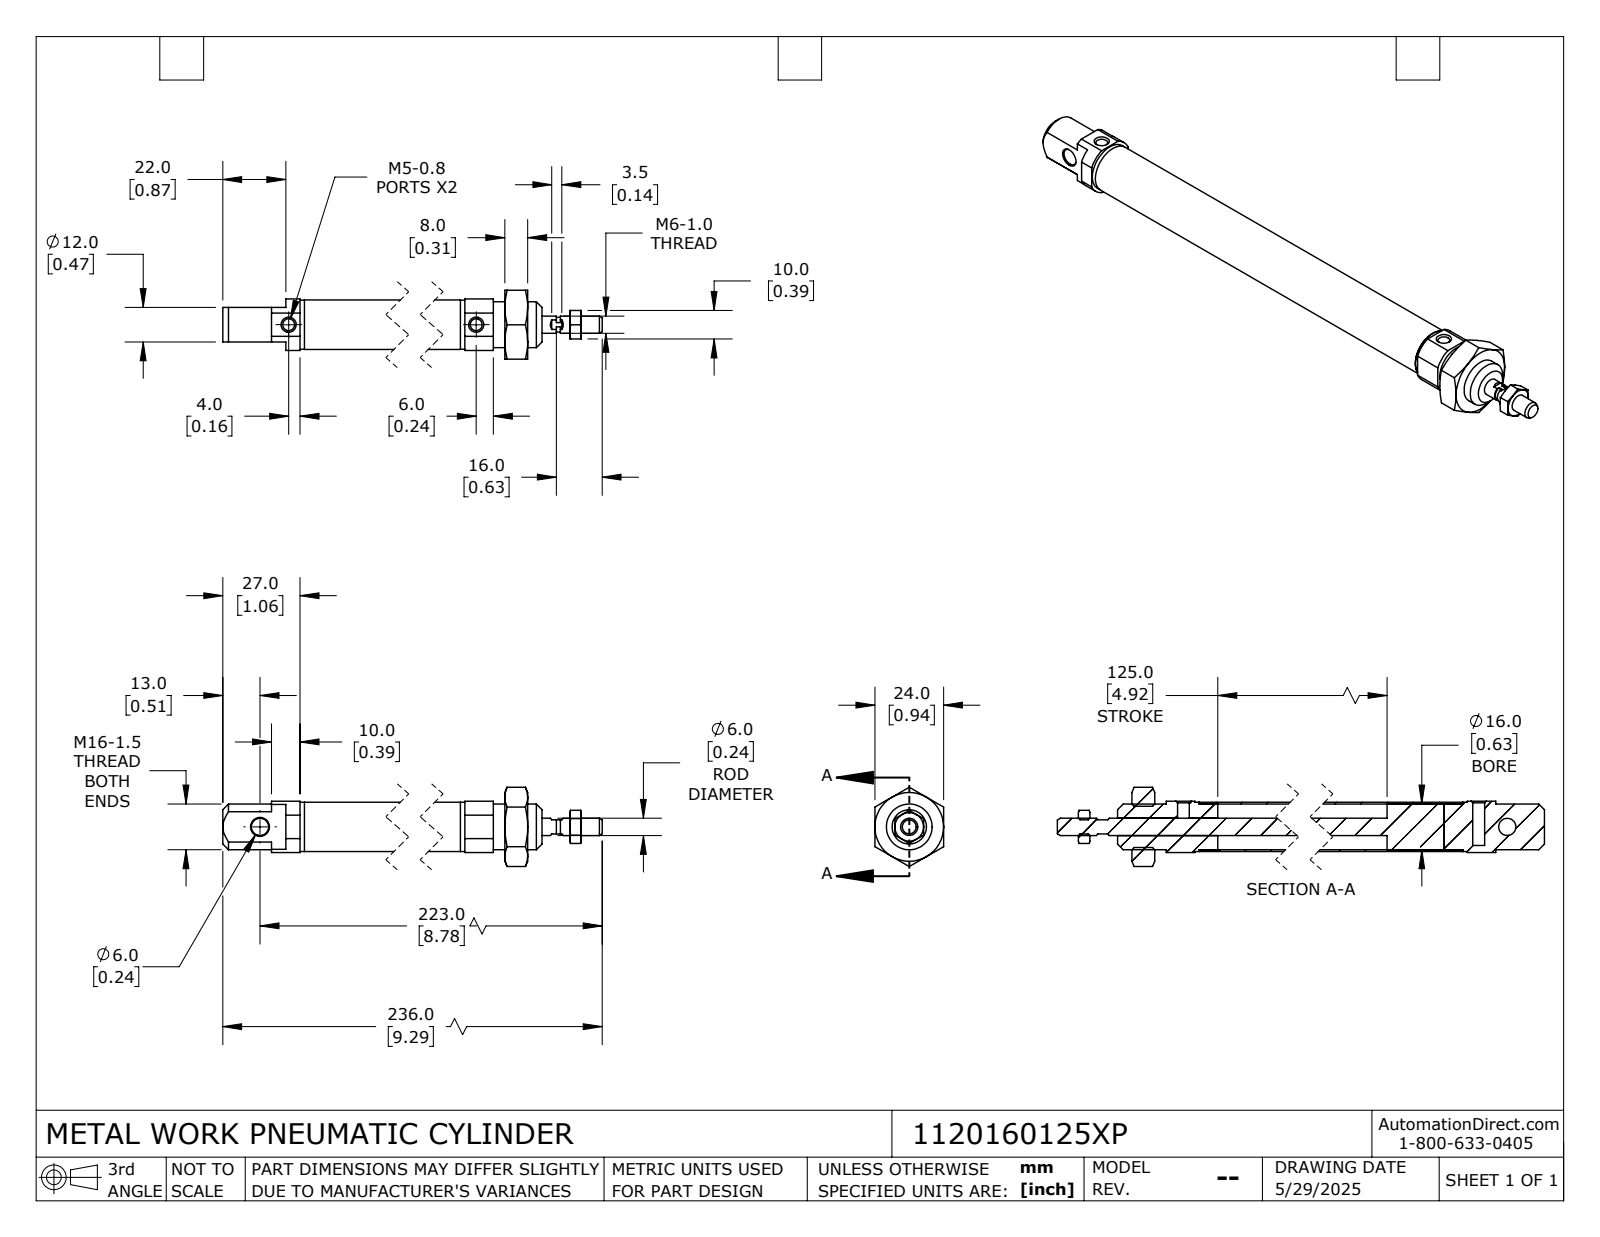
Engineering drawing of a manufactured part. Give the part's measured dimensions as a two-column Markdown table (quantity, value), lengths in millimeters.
| quantity | value |
| --- | --- |
| part name | 1120160125XP_ROD; 1120160125XP_BODY; 1120160125XP |
| STEP written by | SolidWorks 2024 (CONFIG_CONTROL_DESIGN) |
| units | millimeters |
| bodies | 6 solids, 146 faces (55 planar, 45 cylindrical, 46 other) |
| overall size | 236 × 27.71 × 24 |
| volume | 30 534 mm³ |
| surface area | 29 082 mm² |
| round holes (diameter × count) | 4.13 × 2, 4.92 × 1, 6 × 1, 14.38 × 1 |
| round bosses / shafts (diameter × count) | 17.27 × 1, 17.2 × 1, 16.15 × 1, 16 × 1, 6 × 1, 5.2 × 1 |
| partial cylindrical surfaces (radius × count) | 9.85 × 1 |
| main face-to-face distances | 8, 18, 24, 22, 175, 12, 180, 17, 167, 2.97 |
| hole center spacings | 169 |
